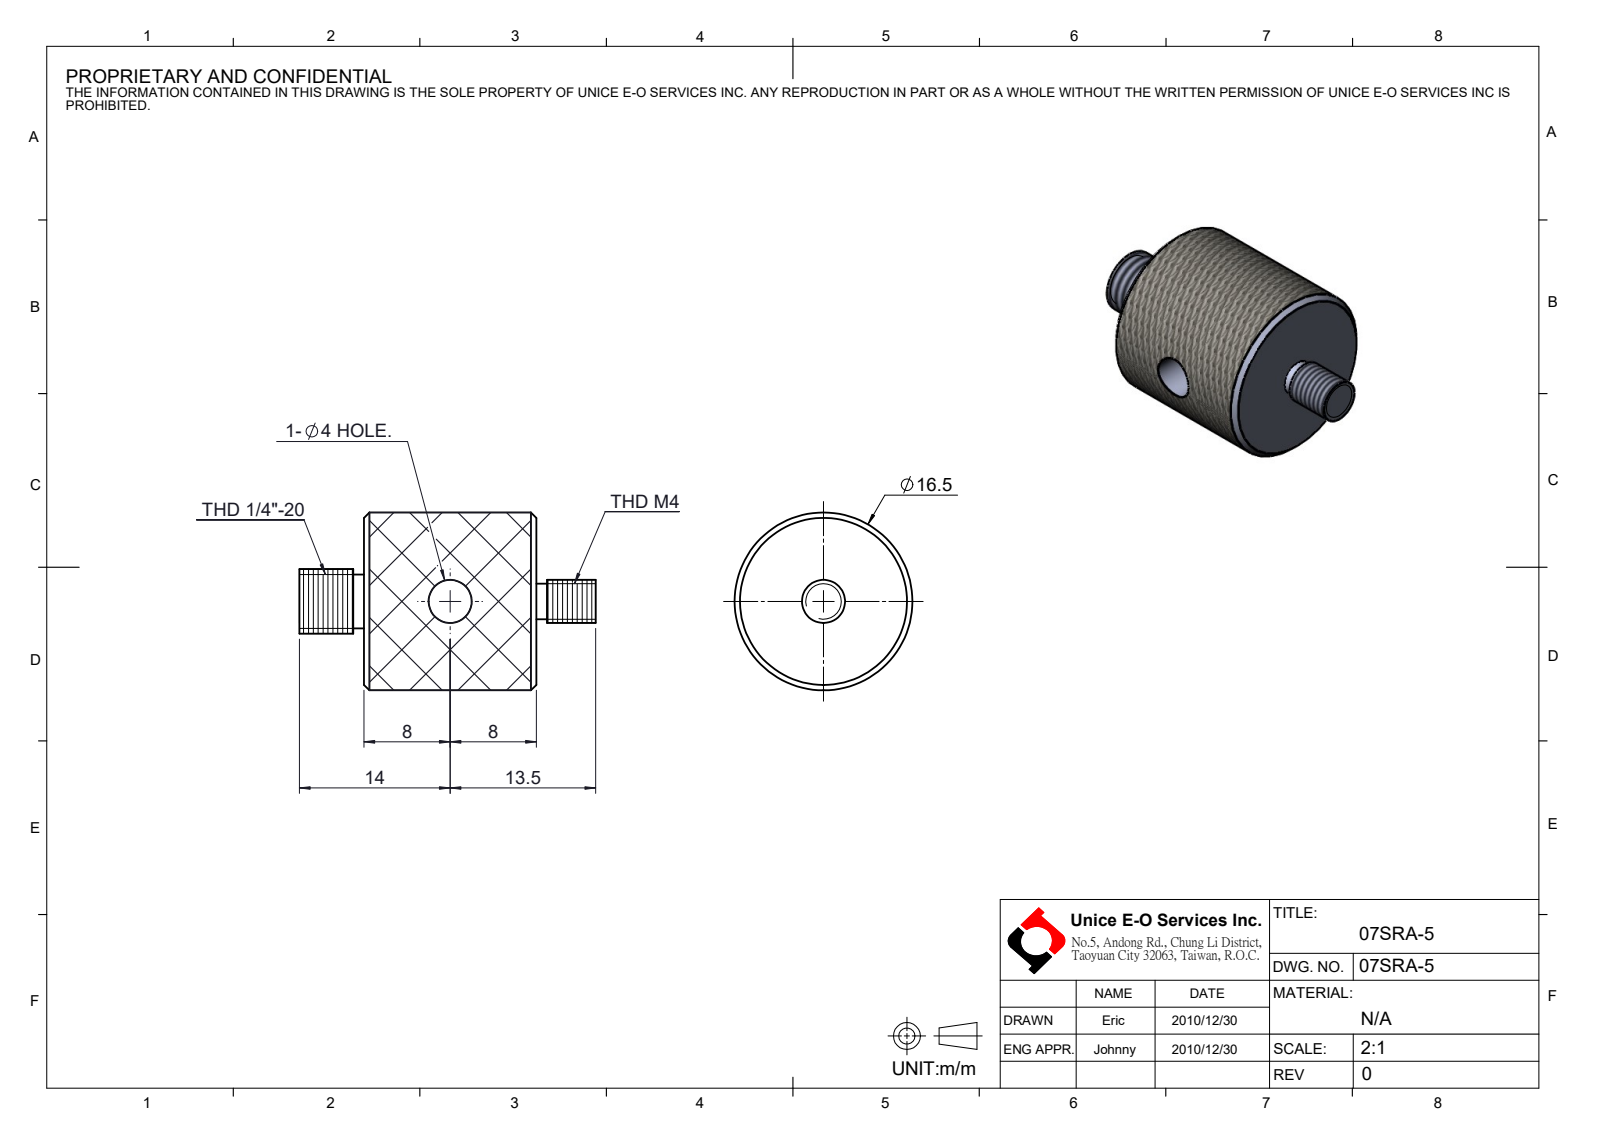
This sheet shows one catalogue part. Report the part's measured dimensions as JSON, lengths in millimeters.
{"part_name": "07SRA-5", "step_written_by": "SolidWorks 2016 (CONFIG_CONTROL_DESIGN)", "units": "millimeters", "bodies": {"solids": 1, "faces": 22, "planar": 6, "cylindrical": 12, "other": 4}, "overall_size": [27.5, 16.5, 16.5], "volume_mm3": 3429, "surface_area_mm2": 1607, "round_holes": [[4, 1]], "round_bosses_or_shafts": [[16.5, 1], [6, 1], [5, 1], [4, 1], [3.3, 1]], "face_to_face_distances": [16, 22, 6, 1, 17, 5.5, 21.5, 27.5, 22.5, 5]}
